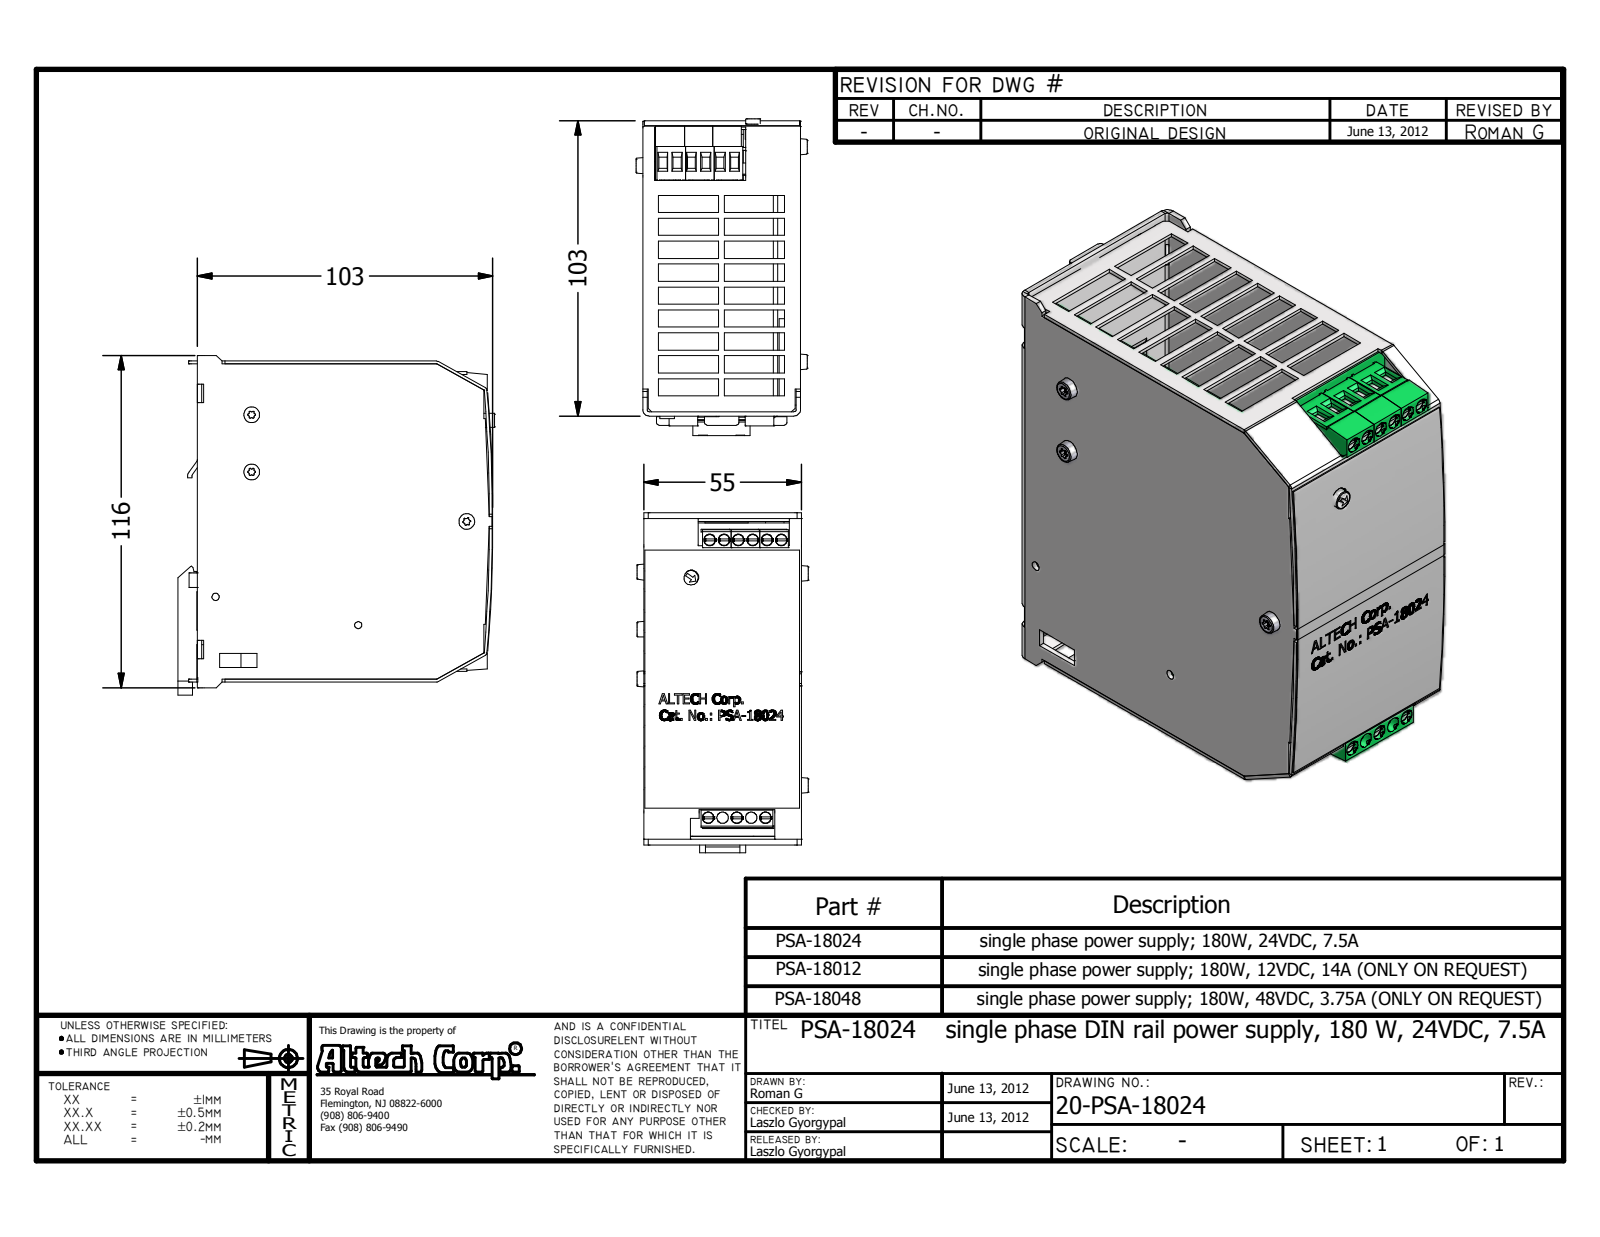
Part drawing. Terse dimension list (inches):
name: ALTECH-PSA-18024
written by: Autodesk Inventor 2013 (CONFIG_CONTROL_DESIGN)
unit: in
bodies: 1 solid, 2147 faces (1520 planar, 400 cylindrical, 227 other)
size: 4.671 × 4.354 × 2.354
volume: 5.765 in³; area: 183.7 in²
holes: 38× ⌀0.039, 11× ⌀0.157, 4× ⌀0.035, 4× ⌀0.091, 3× ⌀0.11, 3× ⌀0.13, 2× ⌀0.079, 2× ⌀0.098, 2× ⌀0.122
bosses: 9× ⌀0.152, 9× ⌀0.055, 5× ⌀0.118, 5× ⌀0.105, 2× ⌀0.185, 2× ⌀0.06, 1× ⌀0.354, 1× ⌀0.197
rounds: 46× R0.004, 31× R0.01, 30× R0.022, 17× R0.02, 16× R0.008, 12× R0.047, 8× R0.039, 8× R0.059
face distances: 0.059, 2.106, 0.063, 2.165, 0.315, 0.311, 1.795, 1.854, 0.374, 1.732
hole spacings: 0.197, 0.1, 3.716, 0.394, 0.591, 3.817, 3.821, 3.823
